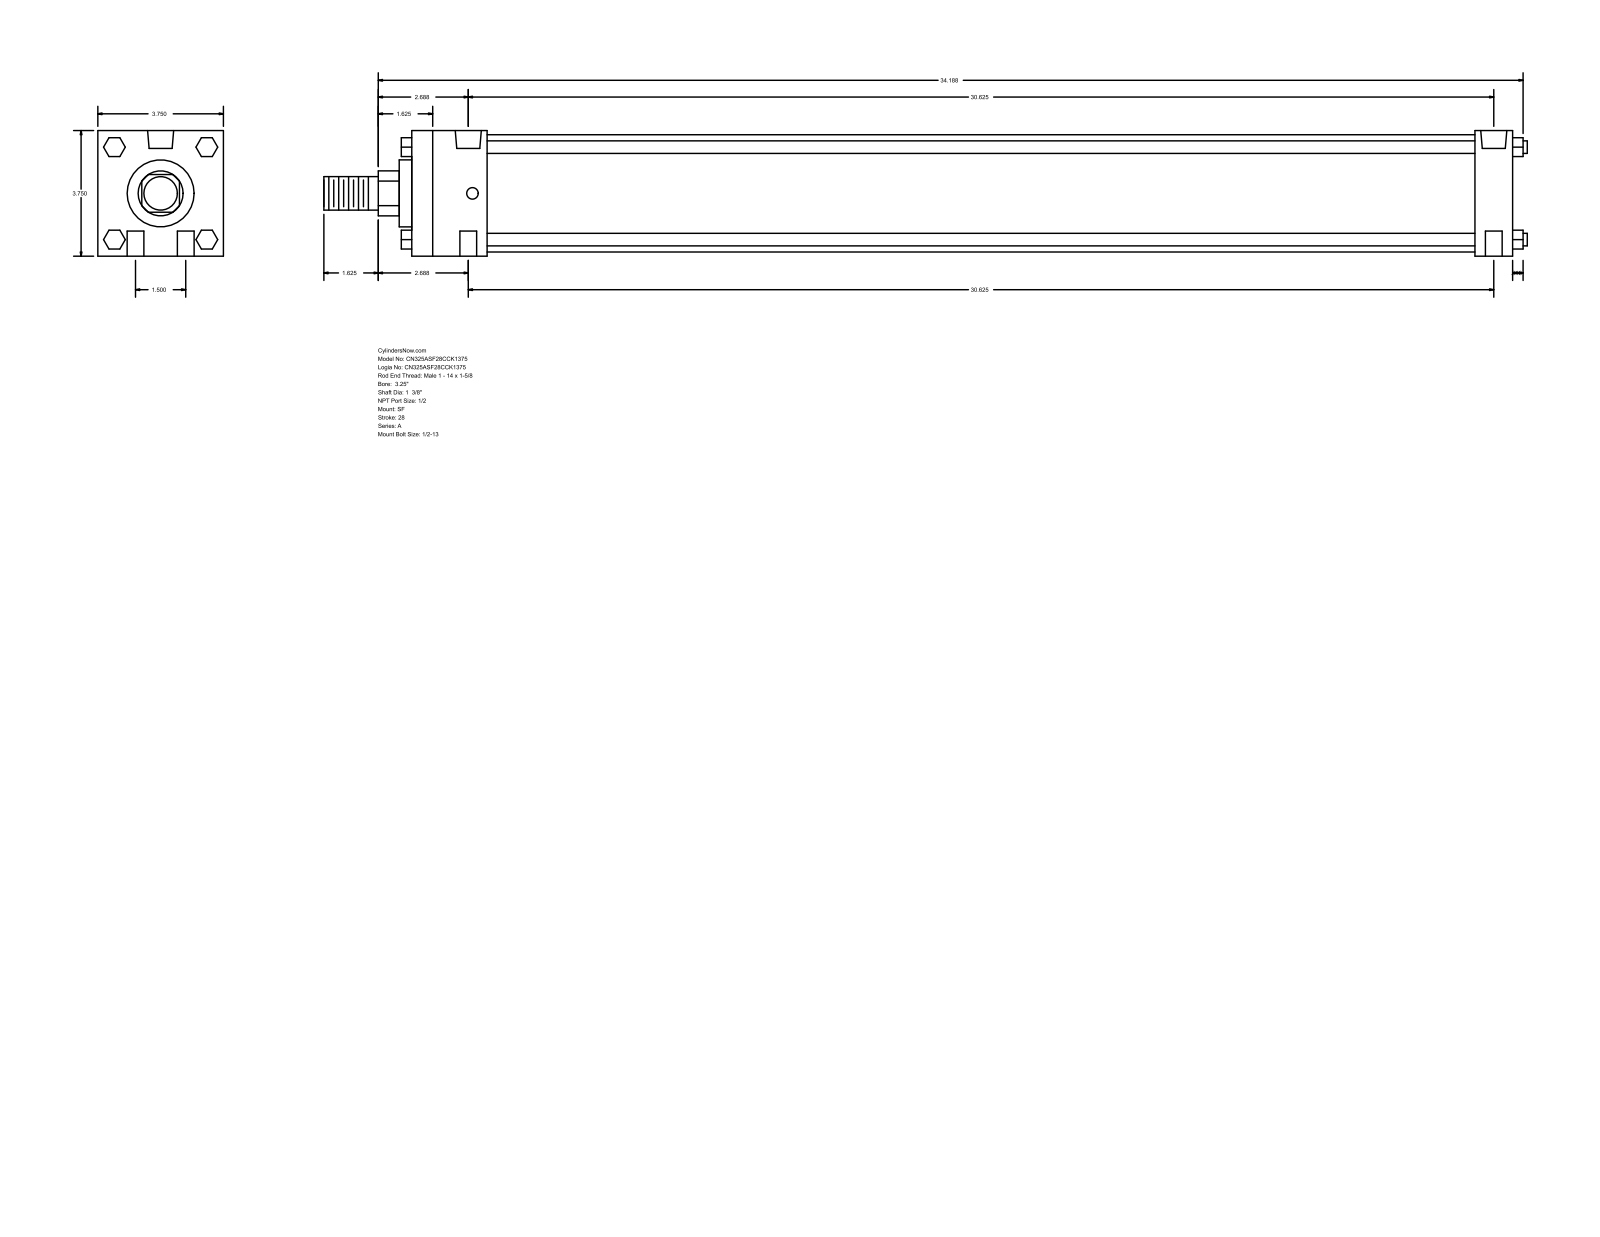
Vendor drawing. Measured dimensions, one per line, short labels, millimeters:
name: A_SF__0325_1.375
written by: GSSL Pune (CONFIG_CONTROL_DESIGN)
unit: mm
bodies: 0 solids, 124 faces (94 planar, 30 cylindrical, 0 other)
size: 912.81 × 95.25 × 95.25
holes: 4× ⌀12.7, 2× ⌀8.73, 2× ⌀19.77
bosses: 4× ⌀9.53, 1× ⌀88.9, 1× ⌀50.8, 1× ⌀34.92, 1× ⌀25.4
rounds: 1× R17.06
face distances: 95.24, 835.02, 57.15, 806.45, 28.57, 749.3, 777.87, 66.67, 9.52, 815.97
hole spacings: 19.05, 778.11, 777.88, 38.1, 778.81, 771.52
